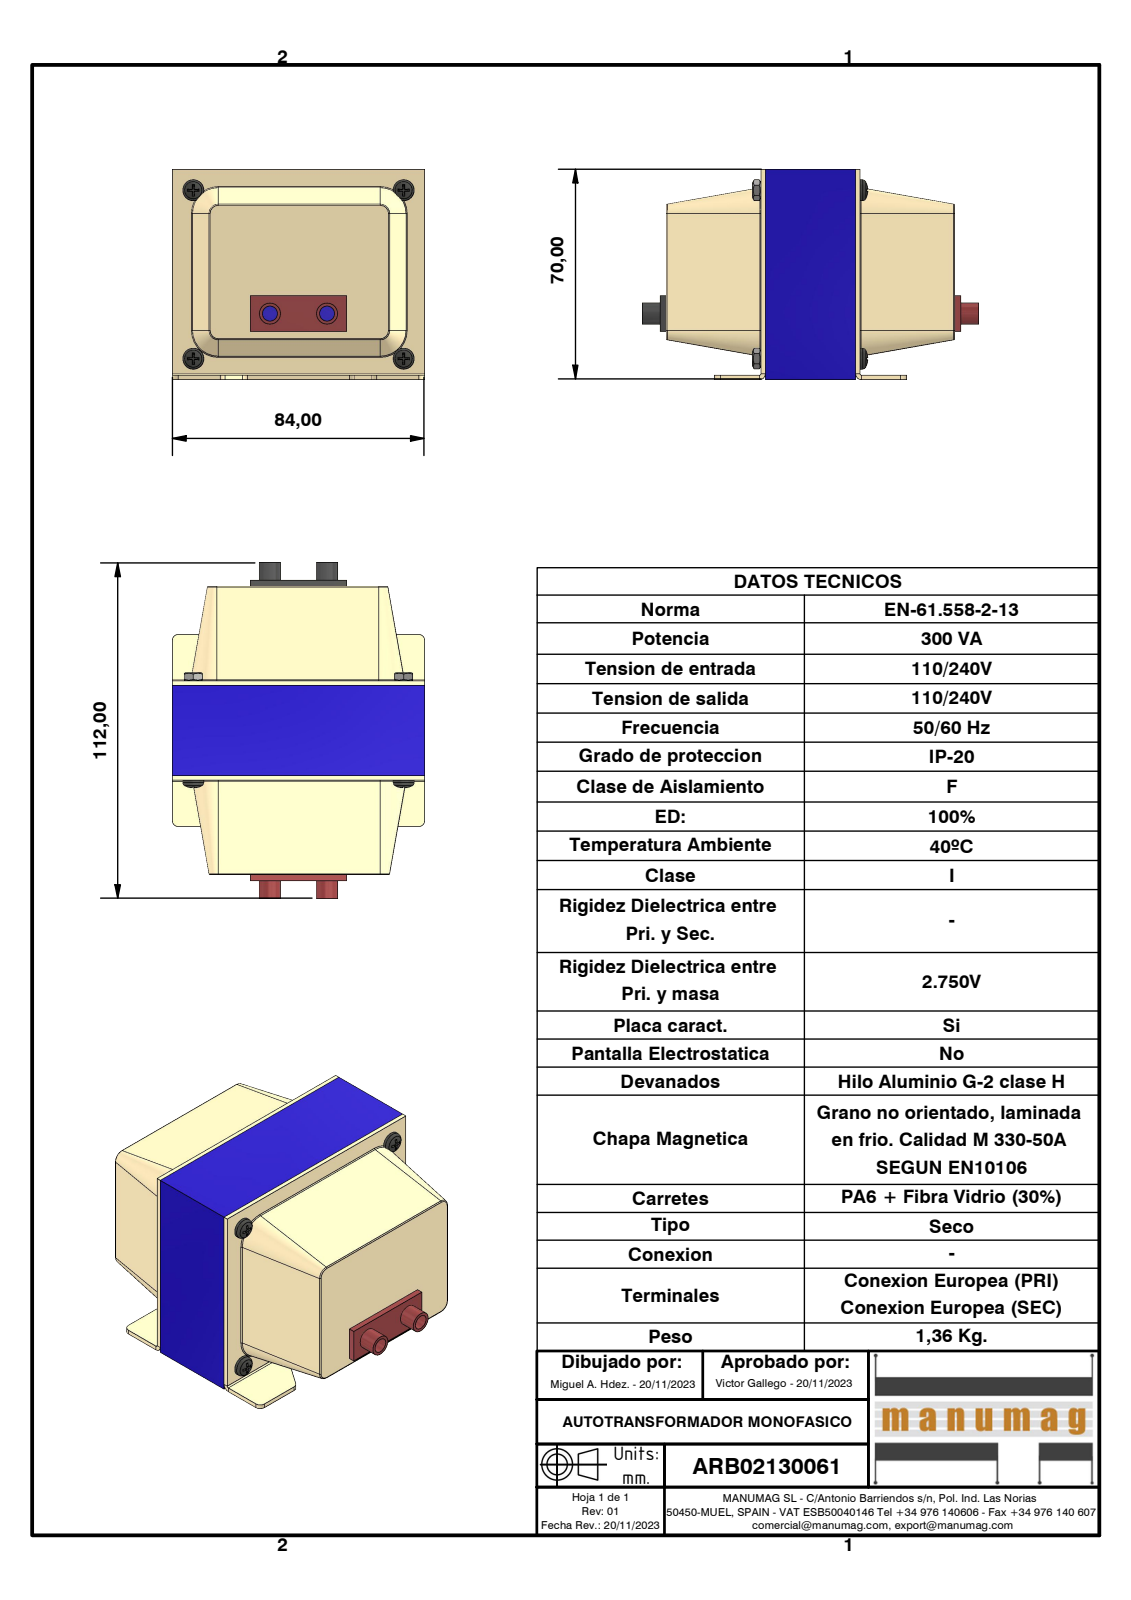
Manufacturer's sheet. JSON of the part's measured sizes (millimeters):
{"part_name": "ARB02130061; EI84 x 70 - 30 (RC28) Azul; TAPA RC28 RECEPTACULO; Receptaculo Rojo (+3 more)", "step_written_by": "Autodesk Inventor 2023 (AUTOMOTIVE_DESIGN)", "units": "millimeters", "bodies": {"solids": 13, "faces": 350, "planar": 162, "cylindrical": 64, "other": 124}, "overall_size": [112, 84, 70], "volume_mm3": 161739, "surface_area_mm2": 82131, "round_holes": [[4, 8], [2.85, 4], [4.5, 4], [5, 2]], "round_bosses_or_shafts": [[3.5, 4], [3.18, 4], [7, 2]], "partial_cylinders_radius": [[0.38, 16], [2, 14], [0.5, 2]], "face_to_face_distances": [31.5, 30, 1.5, 63, 33, 60.77, 14, 56, 70, 94.5], "hole_center_spacings": [70, 89.64, 46.96, 56, 29.58, 29.59, 48.27, 48.28]}
